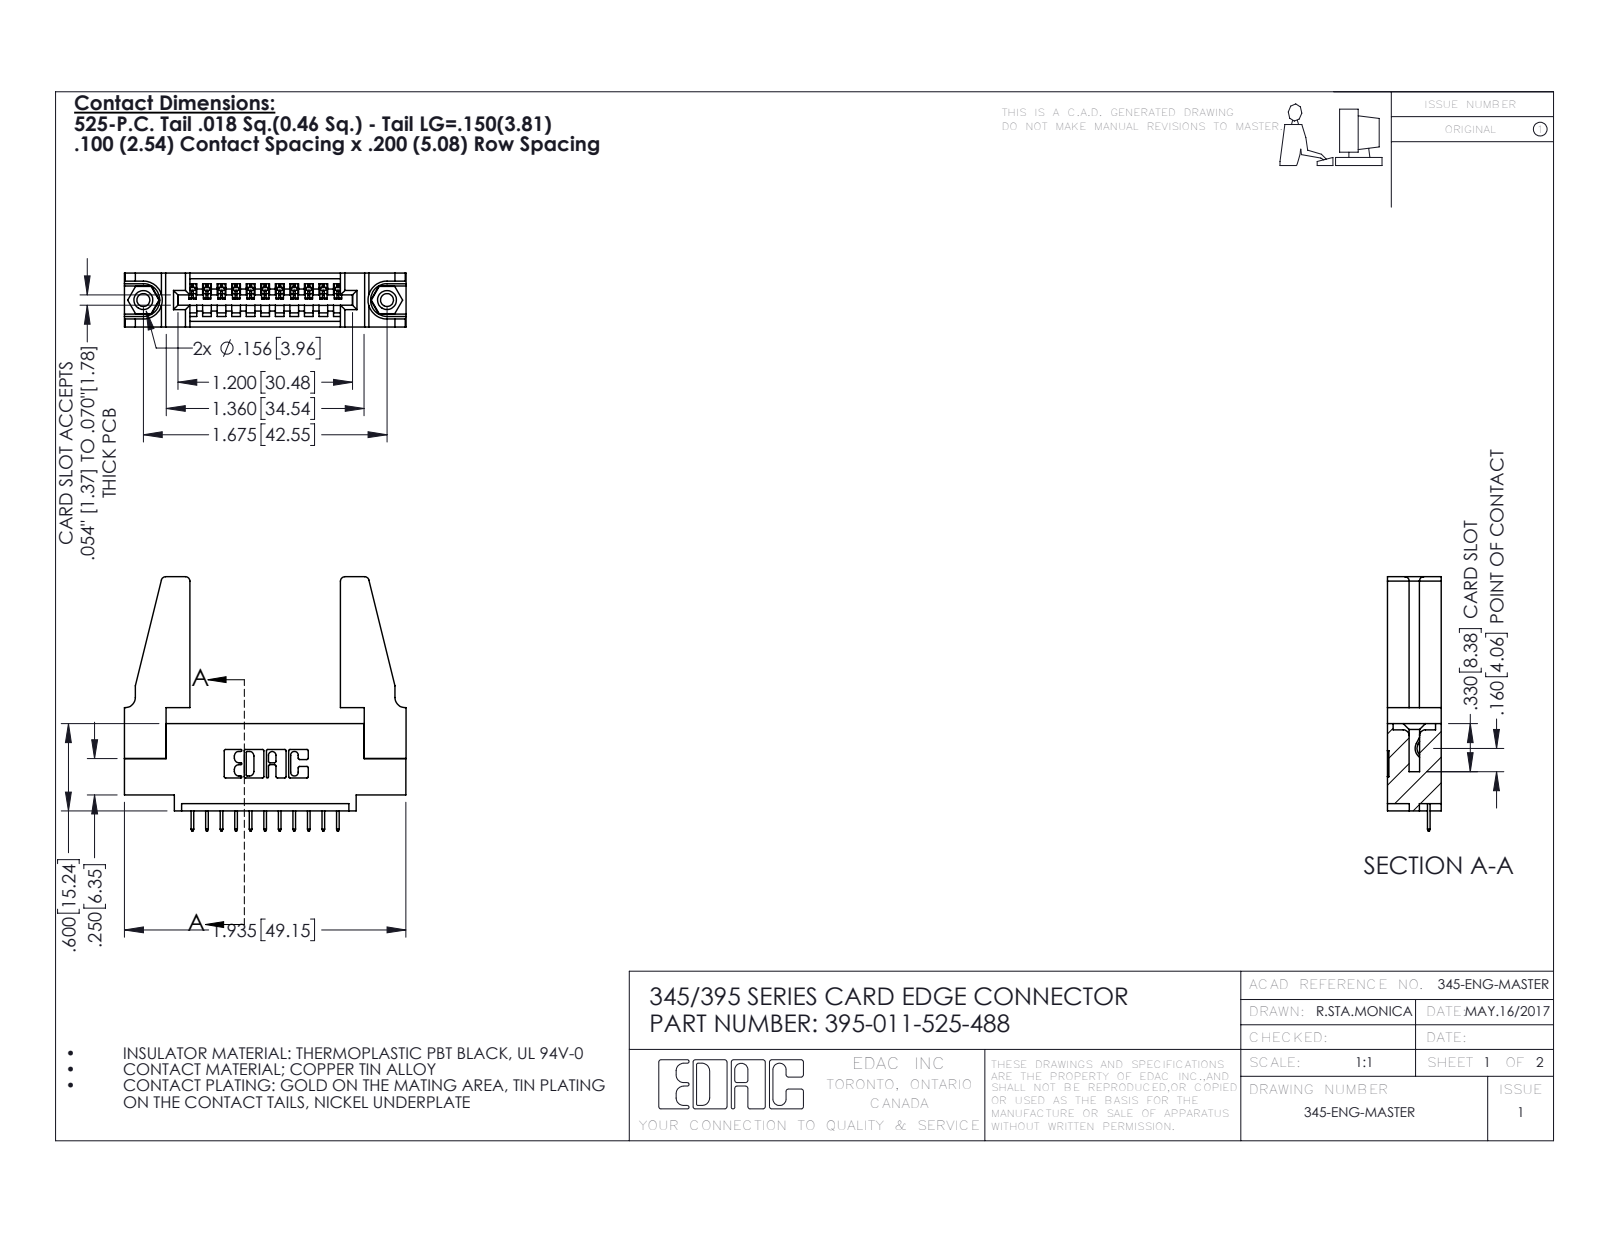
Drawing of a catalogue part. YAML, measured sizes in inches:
part_name: "345-250-001_345-250-001-102; 395-011-525-488; 345-292-001_345-293-125; 345-220-078_345-220-088 (+1 more)"
step_written_by: "SolidWorks 2020 (CONFIG_CONTROL_DESIGN)"
units: inches
bodies: {solids: 16, faces: 936, planar: 662, cylindrical: 258, other: 16}
overall_size: [1.936, 1.747, 0.37]
volume: 0.461
surface_area: 12.95
round_holes:
  - {diameter: 0.089, count: 2}
  - {diameter: 0.125, count: 2}
  - {diameter: 0.156, count: 2}
  - {diameter: 0.064, count: 1}
round_bosses_or_shafts:
  - {diameter: 0.155, count: 2}
partial_cylinders:
  - {radius: 0.006, count: 22}
  - {radius: 0.01, count: 22}
  - {radius: 0.03, count: 8}
  - {radius: 0.007, count: 6}
  - {radius: 0.031, count: 6}
  - {radius: 0.026, count: 3}
  - {radius: 0.031, count: 2}
  - {radius: 0.04, count: 2}
face_to_face_distances: [0.37, 0.072, 0.298, 0.2, 0.098, 0.272, 0.025, 0.225, 0.148, 0.15]
hole_center_spacings: [0.27, 1.443, 1.675]
